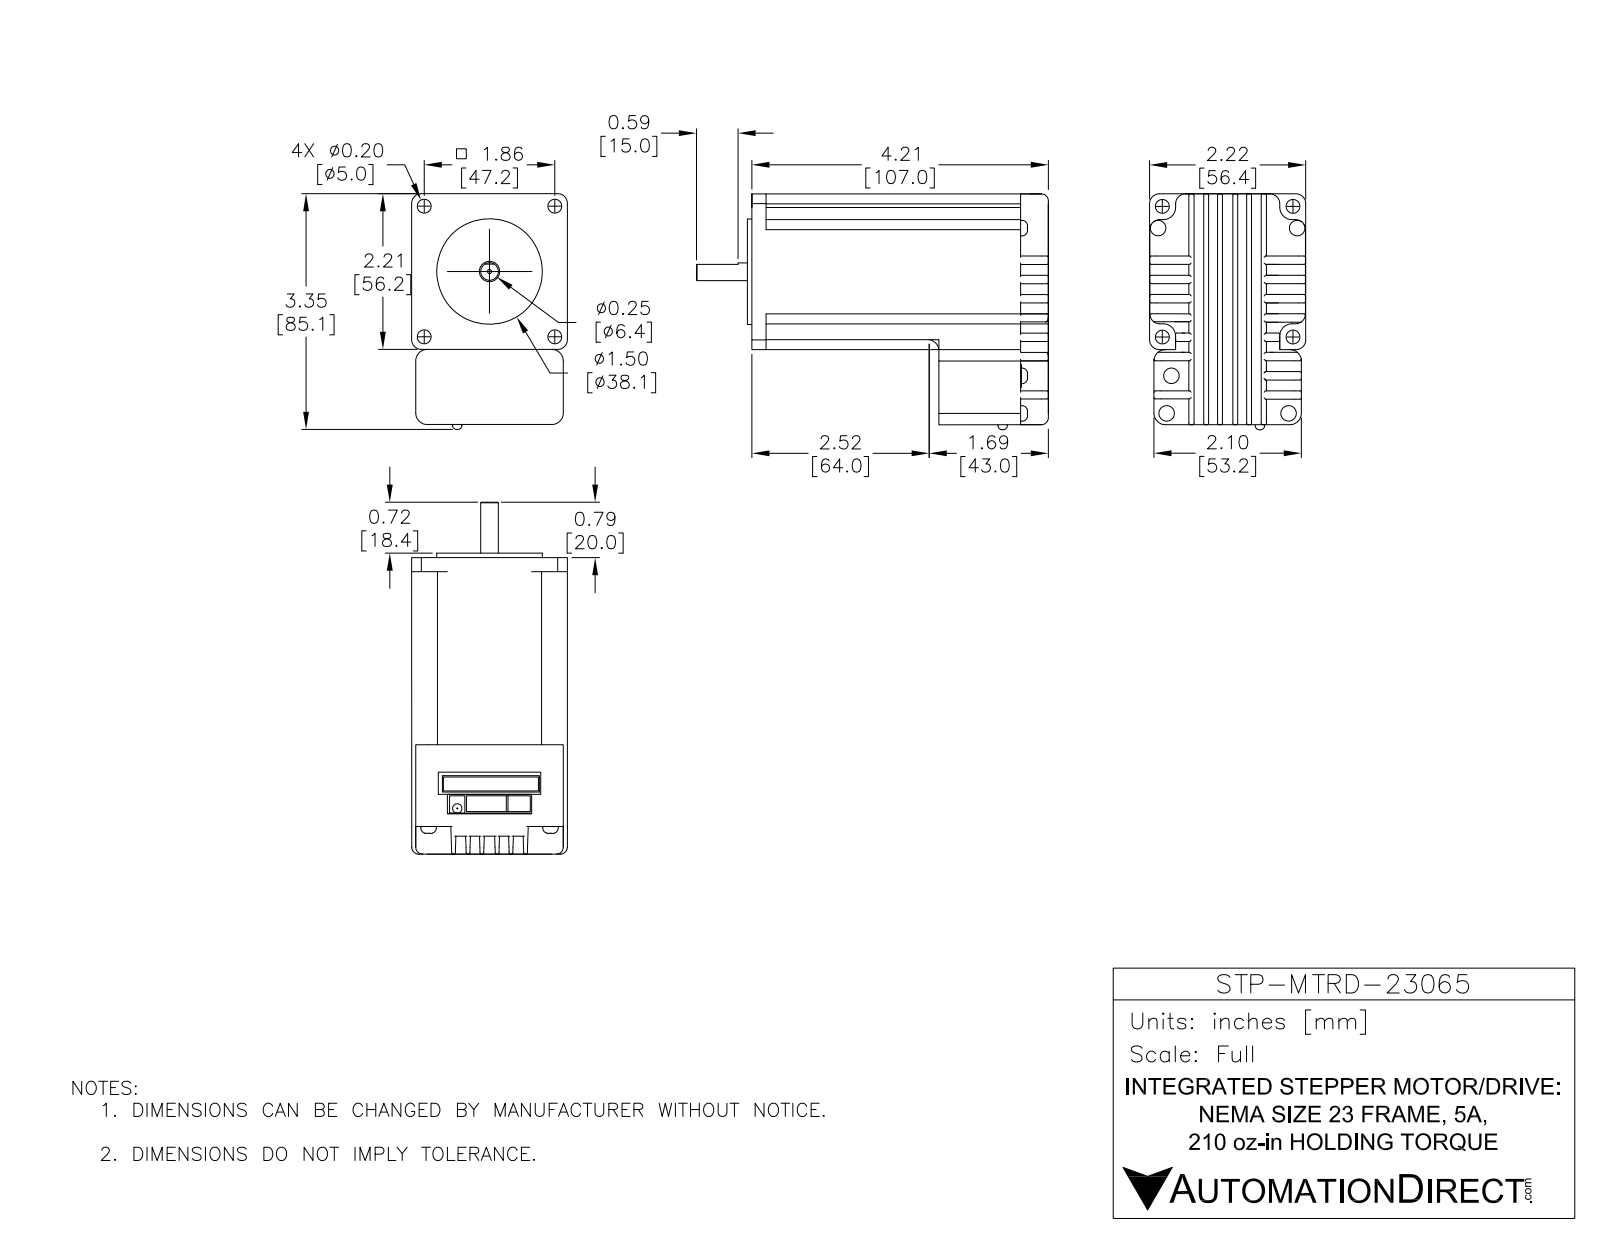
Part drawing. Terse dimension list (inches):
name: STP-MTRD-23065
written by: SolidWorks 2017 (AUTOMOTIVE_DESIGN)
unit: in
bodies: 1 solid, 655 faces (282 planar, 252 cylindrical, 121 other)
size: 5 × 3.339 × 2.213
volume: 20.47 in³; area: 70 in²
holes: 4× ⌀0.197, 1× ⌀0.079, 1× ⌀0.289, 1× ⌀0.748
bosses: 5× ⌀0.22, 4× ⌀0.217, 1× ⌀1.5, 1× ⌀0.315, 1× ⌀0.25
rounds: 87× R0.02, 10× R0.098, 8× R0.142, 5× R0.027, 5× R0.431, 4× R0.126, 4× R0.138, 4× R0.161
face distances: 2.213, 0.196, 0.413, 0.207, 0.403, 0.62, 0.816, 3.957, 1.299, 2.657
hole spacings: 1.312, 1.856, 2.625
